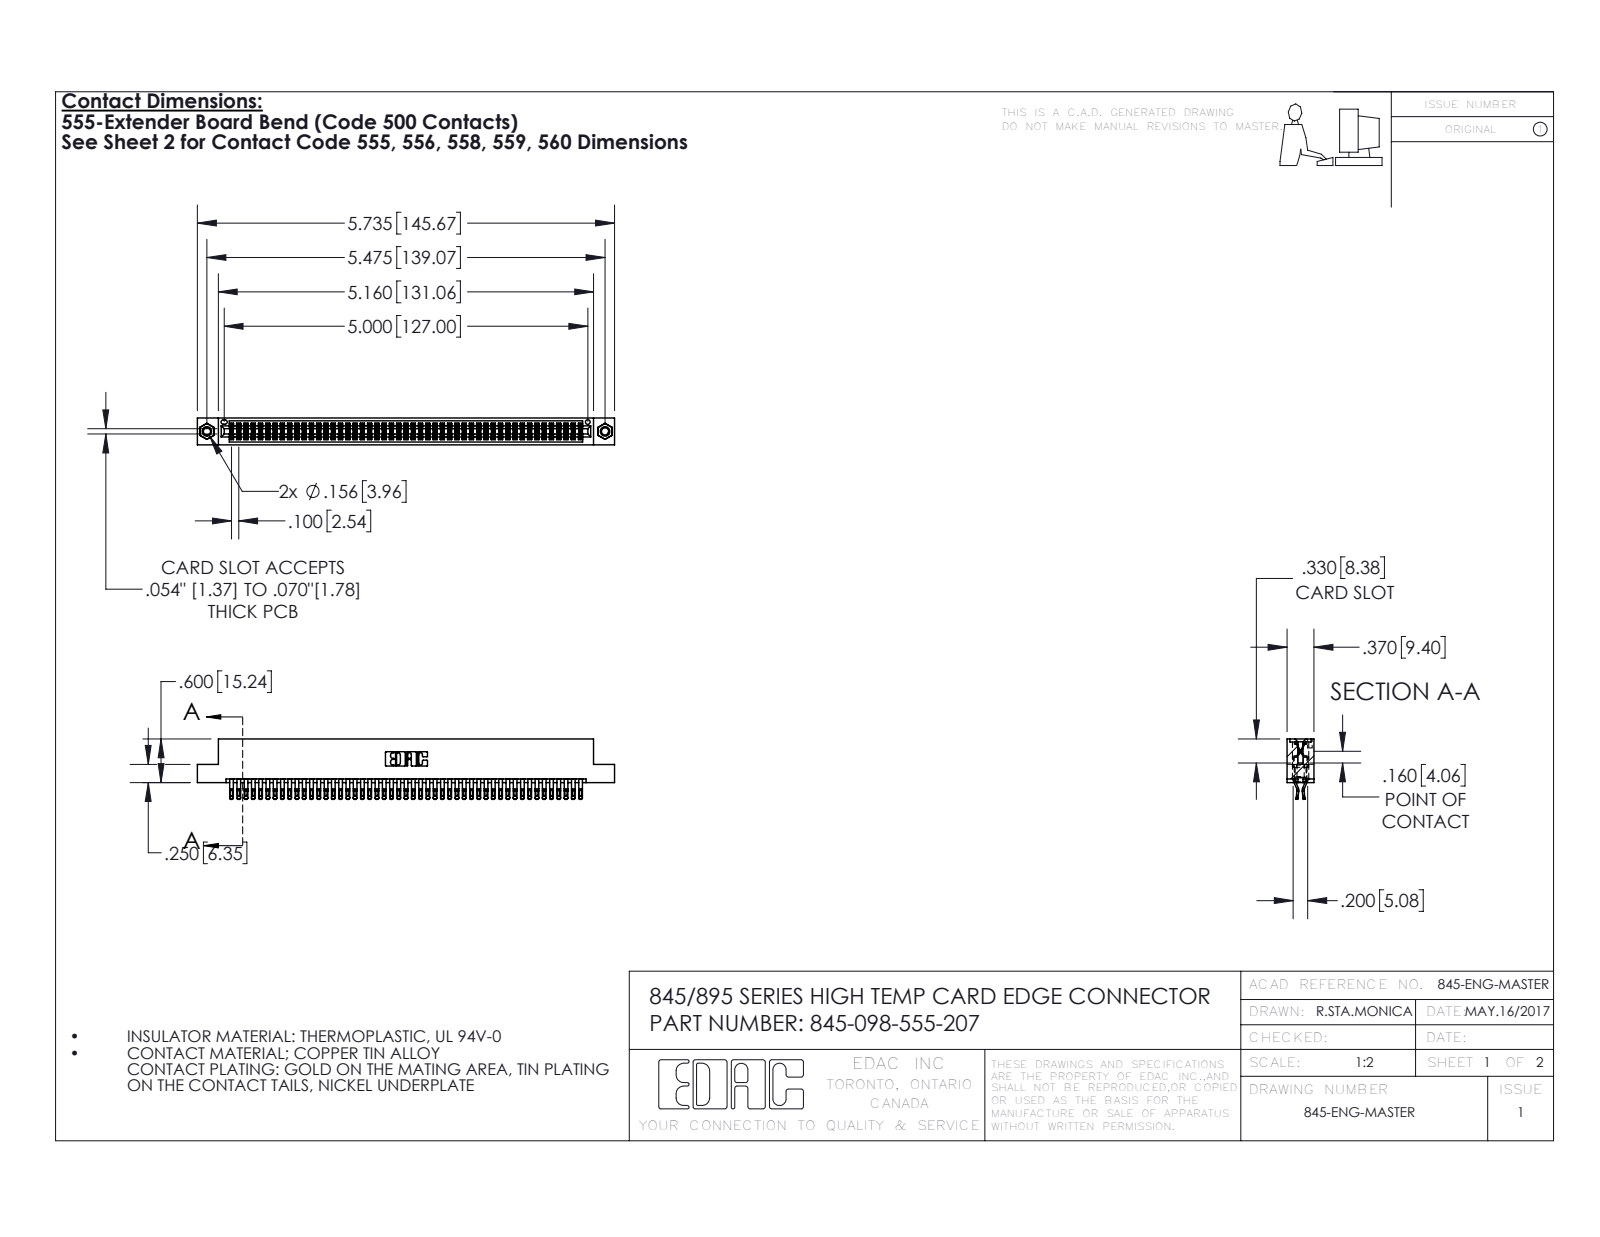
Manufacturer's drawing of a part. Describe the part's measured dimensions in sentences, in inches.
The part is named "345-292-001_555 Tail; 345 Part_Flush Mounting Lugs - 0.156 Dia-TI; 345-098-555-207; 345-250-001_345-250-005-103". Its 3-D file was written by "SolidWorks 2016 (CONFIG_CONTROL_DESIGN)". It is 101 solids with 5674 faces: 3150 planar, 2508 cylindrical and 16 other. Overall it measures 5.735 by 0.832 by 0.37 inches. Its volume is 0.884 cubic inches and its surface area 34.98 square inches. Round holes: 2 of diameter 0.098, 2 of diameter 0.125, 2 of diameter 0.156, 1 of diameter 0.064. Round bosses or shafts: 2 of diameter 0.155. Partial cylindrical surfaces (rounded edges, fillets, slot ends): 245 of radius 0.016, 196 of radius 0.02, 147 of radius 0.006, 22 of radius 0.01, 6 of radius 0.007, 6 of radius 0.031, 3 of radius 0.026, 2 of radius 0.01. The main face-to-face distances are 0.072, 0.298, 0.025, 0.2, 0.37, 0.098, 0.272, 0.225, 0.175, 0.149. The hole center spacings are 0.27, 5.239, 5.475.
